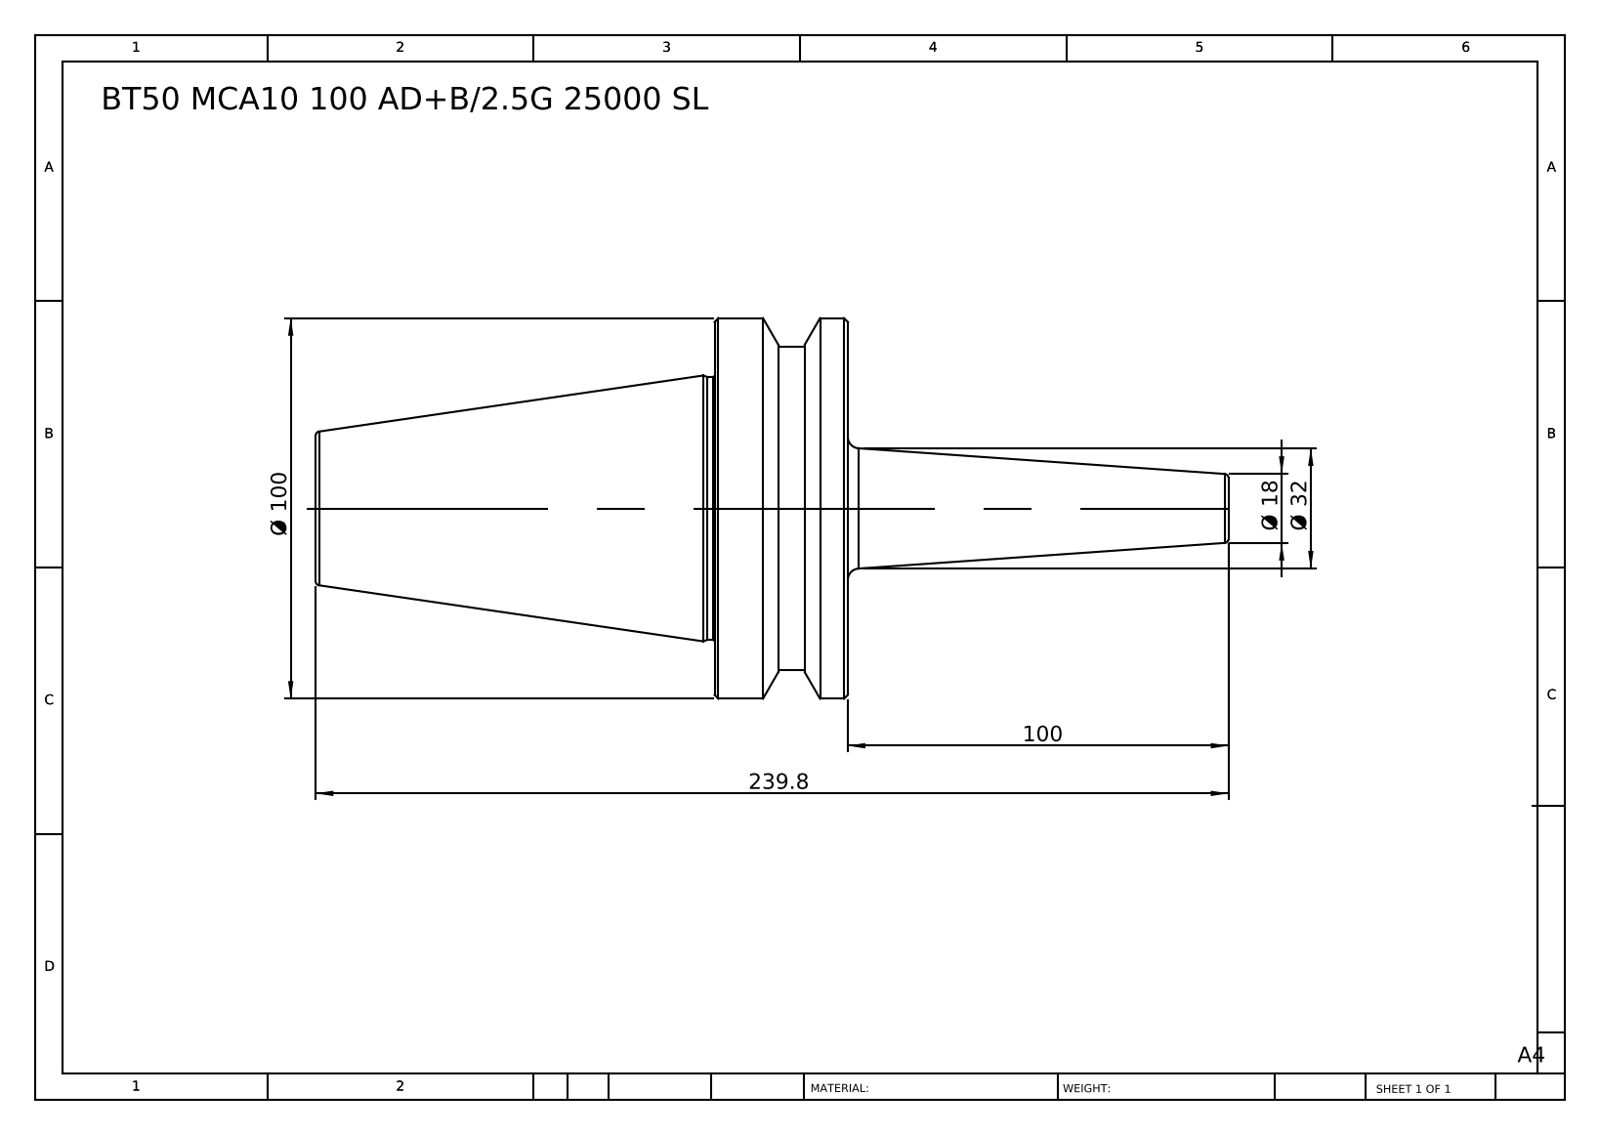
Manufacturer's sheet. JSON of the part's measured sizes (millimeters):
{"part_name": "BT50 MCA10 100 AD+B-2.5G 25000 SL", "step_written_by": "SolidWorks 2014 (CONFIG_CONTROL_DESIGN)", "units": "millimeters", "bodies": {"solids": 1, "faces": 36, "planar": 6, "cylindrical": 8, "other": 22}, "overall_size": [239.8, 100, 100], "volume_mm3": 560582, "surface_area_mm2": 51560, "round_bosses_or_shafts": [[100, 1], [85, 1], [69, 1]], "face_to_face_distances": [35, 139.8, 104.8, 100, 135, 239.8, 111.3, 11.3, 23.7, 128.5]}
